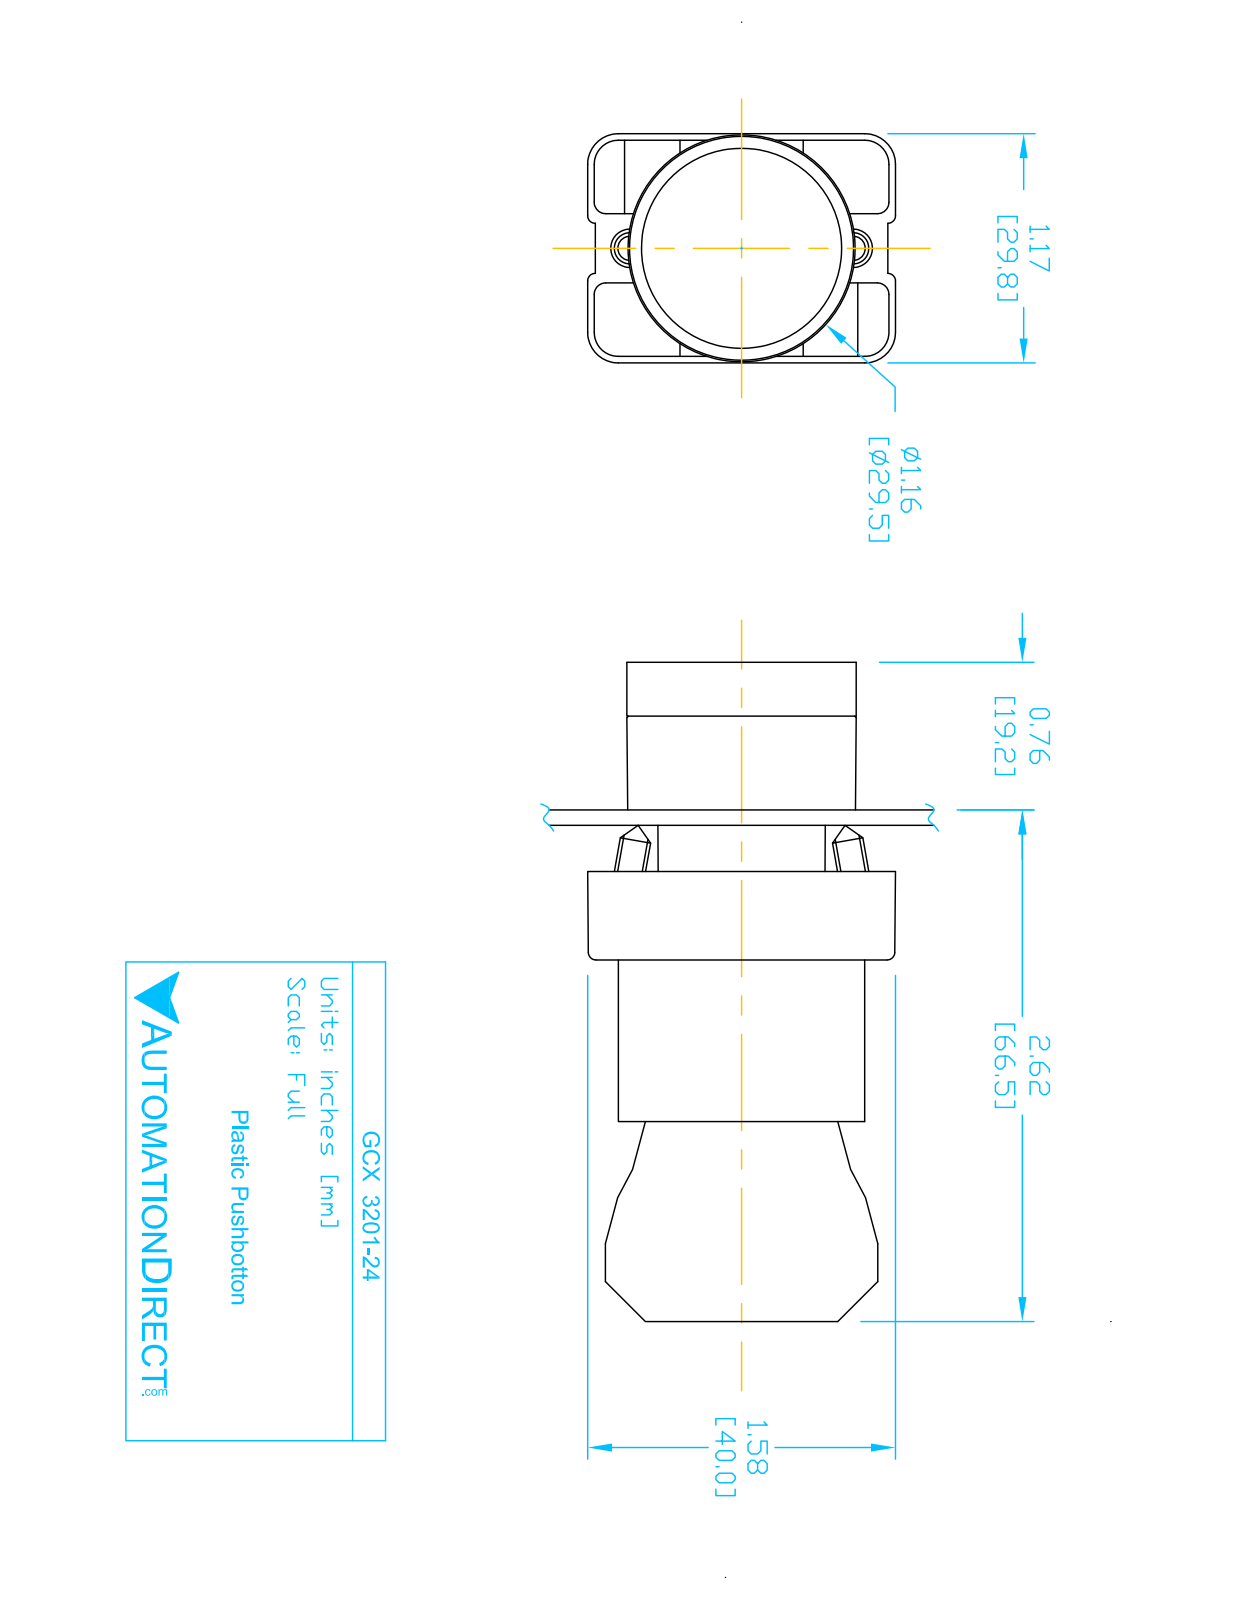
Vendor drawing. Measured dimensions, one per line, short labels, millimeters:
name: ECX3029-2; ecx1030; GCX3201-24; GCX3201 OPERATOR (+1 more)
written by: SolidWorks 2016 (AUTOMOTIVE_DESIGN)
unit: mm
bodies: 8 solids, 431 faces (252 planar, 148 cylindrical, 31 other)
size: 84.3 × 40.2 × 29.9
volume: 45 790 mm³; area: 25 010 mm²
holes: 2× ⌀2, 2× ⌀3.1, 2× ⌀3.3, 1× ⌀2.2, 1× ⌀5, 1× ⌀11.9, 1× ⌀22.3, 1× ⌀22.6, 1× ⌀26
bosses: 4× ⌀4, 1× ⌀29.8, 1× ⌀25.5, 1× ⌀24, 1× ⌀21.7, 1× ⌀19.8, 1× ⌀12.8
rounds: 24× R1.5, 12× R1, 12× R3.1, 12× R4, 8× R1, 2× R3.3, 1× R0.5, 1× R1.6
face distances: 21, 14.7, 51.3, 30.3, 29.7, 7, 58.3, 37.3, 0.8, 0.8
hole spacings: 6, 13.8, 12, 12.4
